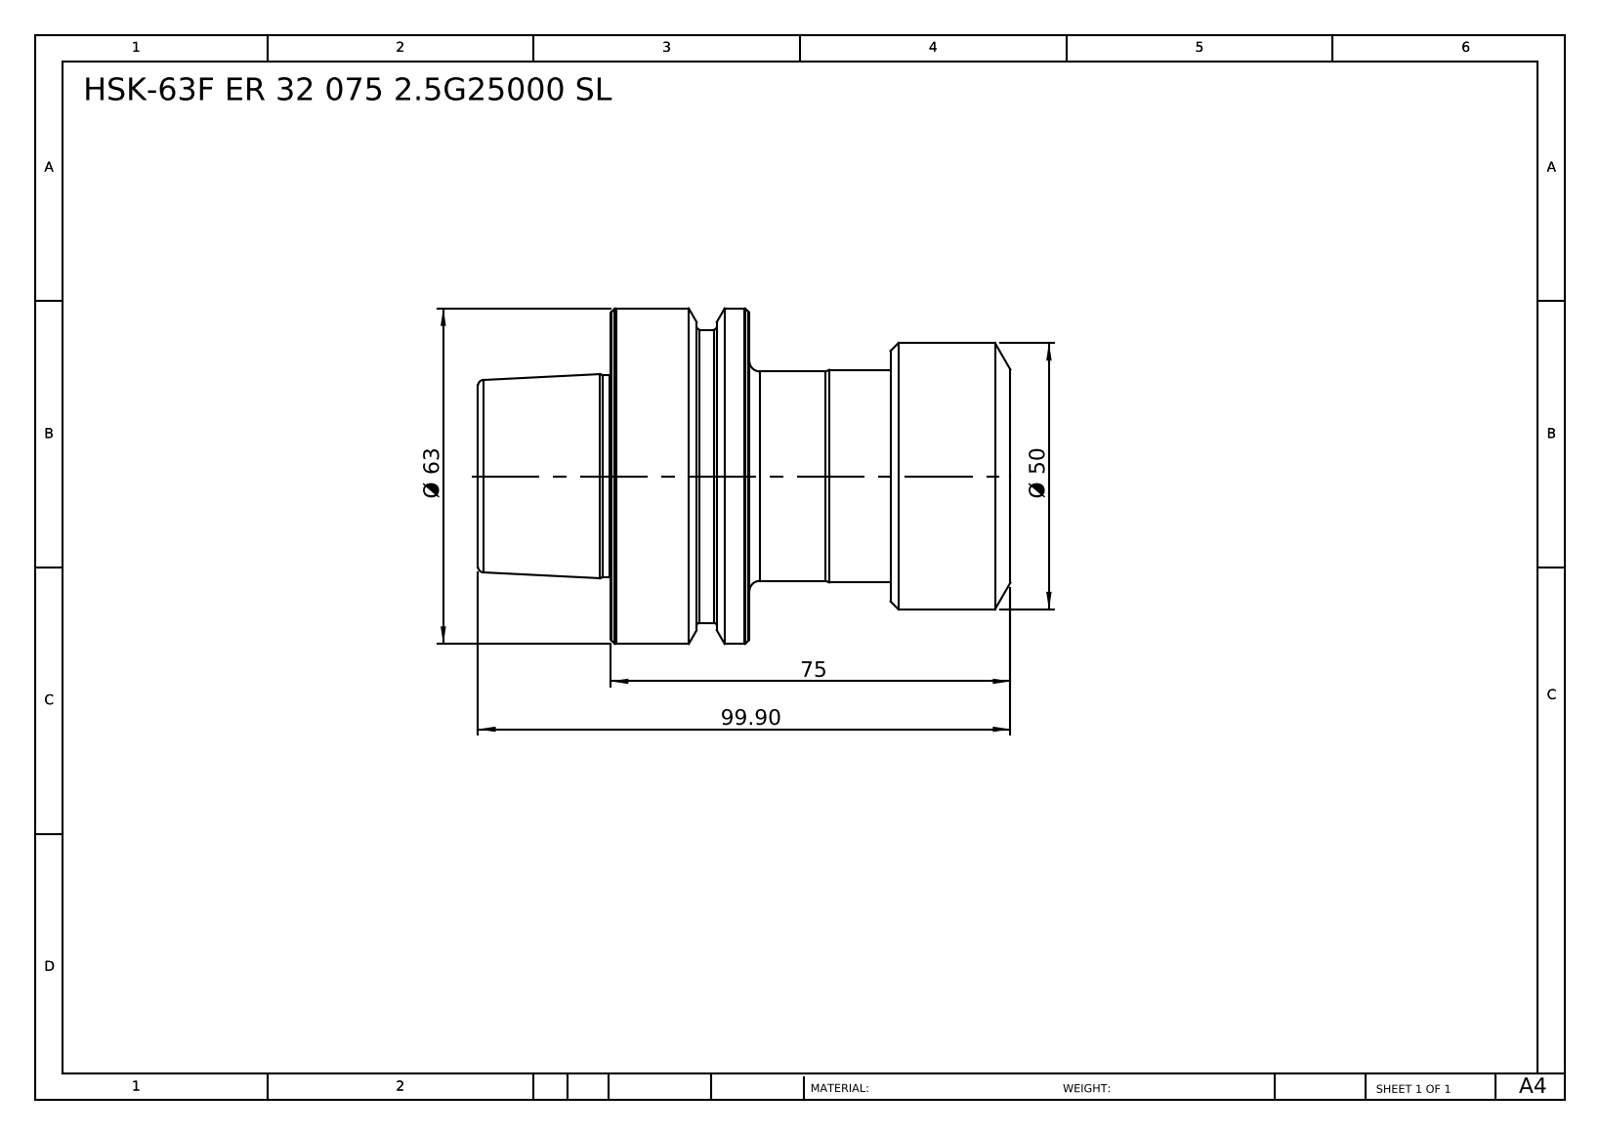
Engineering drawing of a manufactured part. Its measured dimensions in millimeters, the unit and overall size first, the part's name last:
Units: millimetres
Overall size (bounding box): 99.9 × 63 × 63
Round bosses / shafts (diameter × count): ⌀63 ×1, ⌀55 ×1, ⌀50 ×1, ⌀39.9 ×1, ⌀39.3 ×1, ⌀37.8 ×1
Main face-to-face distances: 26, 49, 75, 99.9, 50.9, 24.9, 22.5, 26.5, 52.5, 77.4
Volume: 180 091 mm³ · Surface area: 22 541 mm²
Bodies: 1 solid, 59 faces (7 planar, 14 cylindrical, 38 other)
Part name (STEP PRODUCT): HSK-63F ER 32 075 2.5G25000 SL
STEP written by: SolidWorks 2014 (CONFIG_CONTROL_DESIGN)
